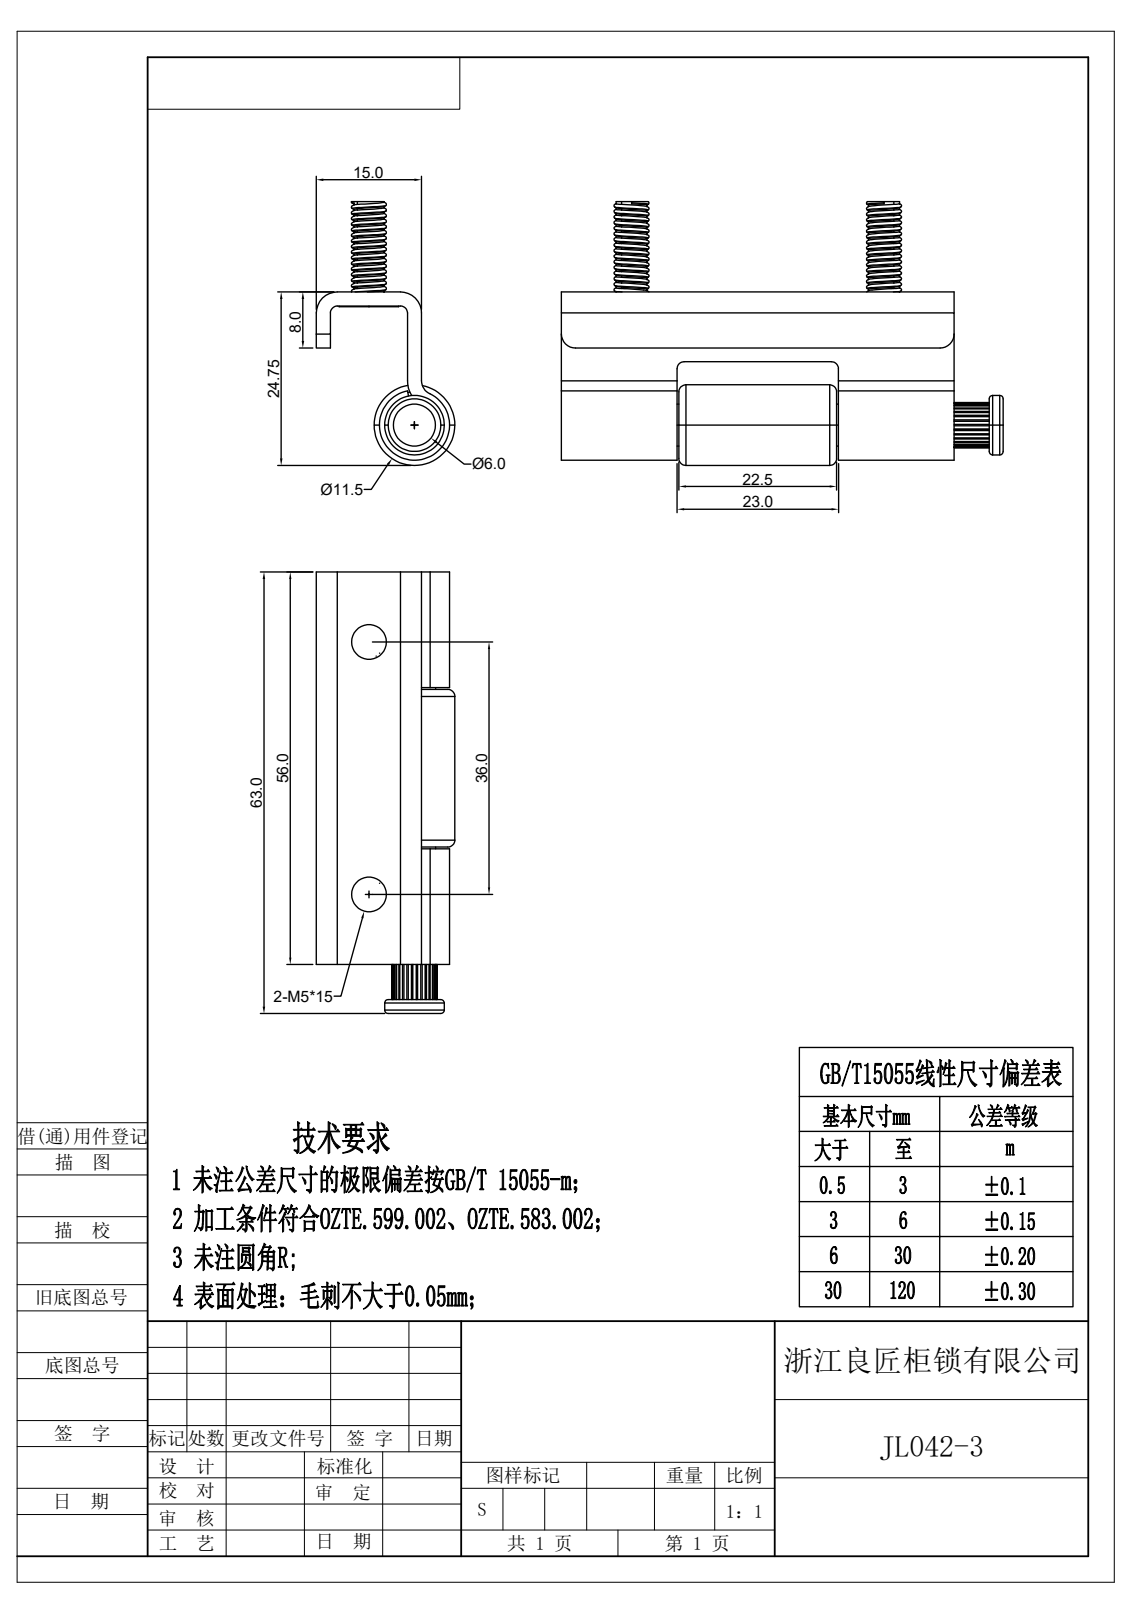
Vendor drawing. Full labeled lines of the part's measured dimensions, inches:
STEP written by: Rhino 8.5 (CONFIG_CONTROL_DESIGN)
Units: inches
Bodies: 5 solids, 233 faces (39 planar, 104 cylindrical, 90 other)
Overall size (bounding box): 2.48 × 1.482 × 0.778
Volume: 0.526 in³ · Surface area: 13.96 in²
Round holes (diameter × count): ⌀0.135 ×2, ⌀0.335 ×2, ⌀0.236 ×1, ⌀0.256 ×1
Round bosses / shafts (diameter × count): ⌀0.453 ×1, ⌀0.394 ×1, ⌀0.335 ×1
Partial cylindrical surfaces — rounded edges, fillets, slot ends (radius × count): R0.004 ×30, R0.039 ×4, R0.079 ×3, R0.118 ×2, R0.127 ×1, R0.157 ×1
Main face-to-face distances: 0.079, 0.512, 0.591, 0.433, 0.016, 0.063, 0.02, 0.083, 0.65, 1.555
Hole centre spacings: 1.417
